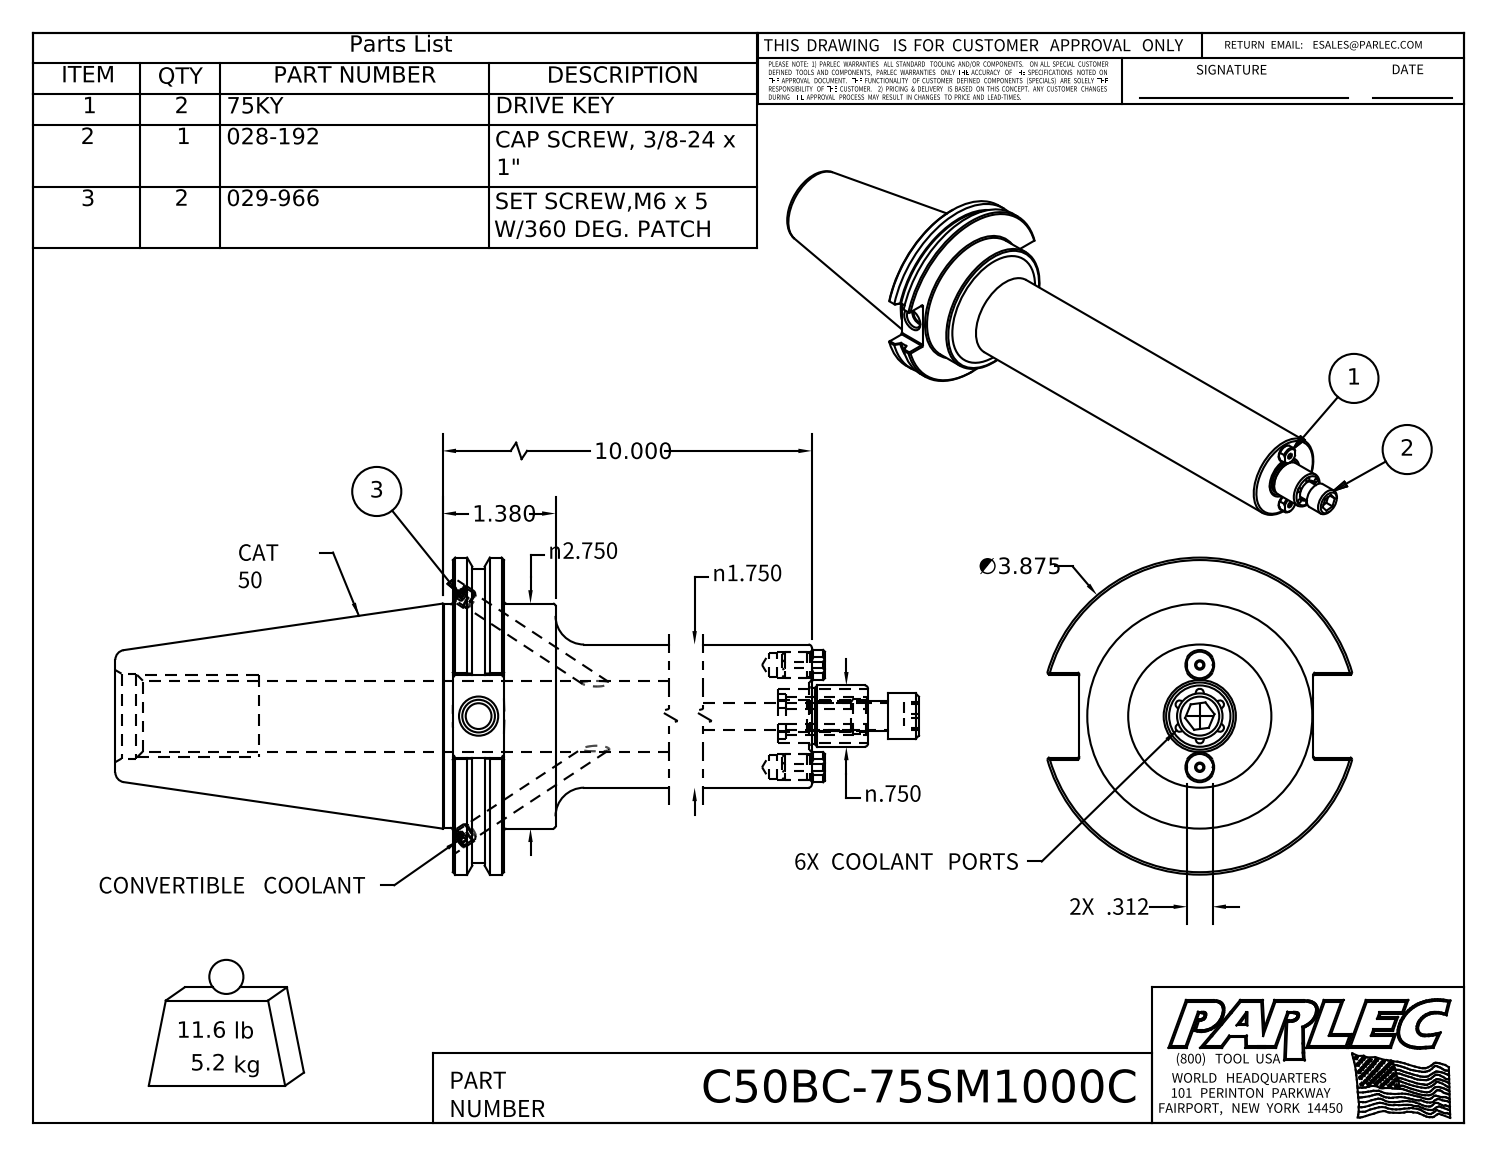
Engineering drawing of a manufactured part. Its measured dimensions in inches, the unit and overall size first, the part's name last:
Units: inches
Overall size (bounding box): 14.687 × 3.875 × 3.729
Round holes (diameter × count): ⌀0.098 ×6, ⌀0.197 ×2, ⌀0.24 ×2, ⌀0.292 ×2, ⌀0.312 ×2, ⌀0.315 ×1, ⌀0.33 ×1, ⌀0.399 ×1, ⌀0.43 ×1, ⌀0.865 ×1, ⌀1.038 ×1
Round bosses / shafts (diameter × count): ⌀3.875 ×1, ⌀3.594 ×1, ⌀2.75 ×1, ⌀2.73 ×1, ⌀1.75 ×1, ⌀0.75 ×1, ⌀0.69 ×1
Partial cylindrical surfaces — rounded edges, fillets, slot ends (radius × count): R0.02 ×12, R0.28 ×1
Main face-to-face distances: 0.625, 9.875, 9.25, 1.255, 0.63, 8.62, 4.125, 4.75, 5.38, 14
Hole centre spacings: 0.285, 0.493, 0.542, 0.806, 0.284, 0.341, 0.569, 0.625
Volume: 40.48 in³ · Surface area: 147.3 in²
Bodies: 1 solid, 129 faces (40 planar, 50 cylindrical, 39 other)
Part name (STEP PRODUCT): C50BC-75SM1000C
STEP written by: Autodesk Inventor 2018 (AUTOMOTIVE_DESIGN)
